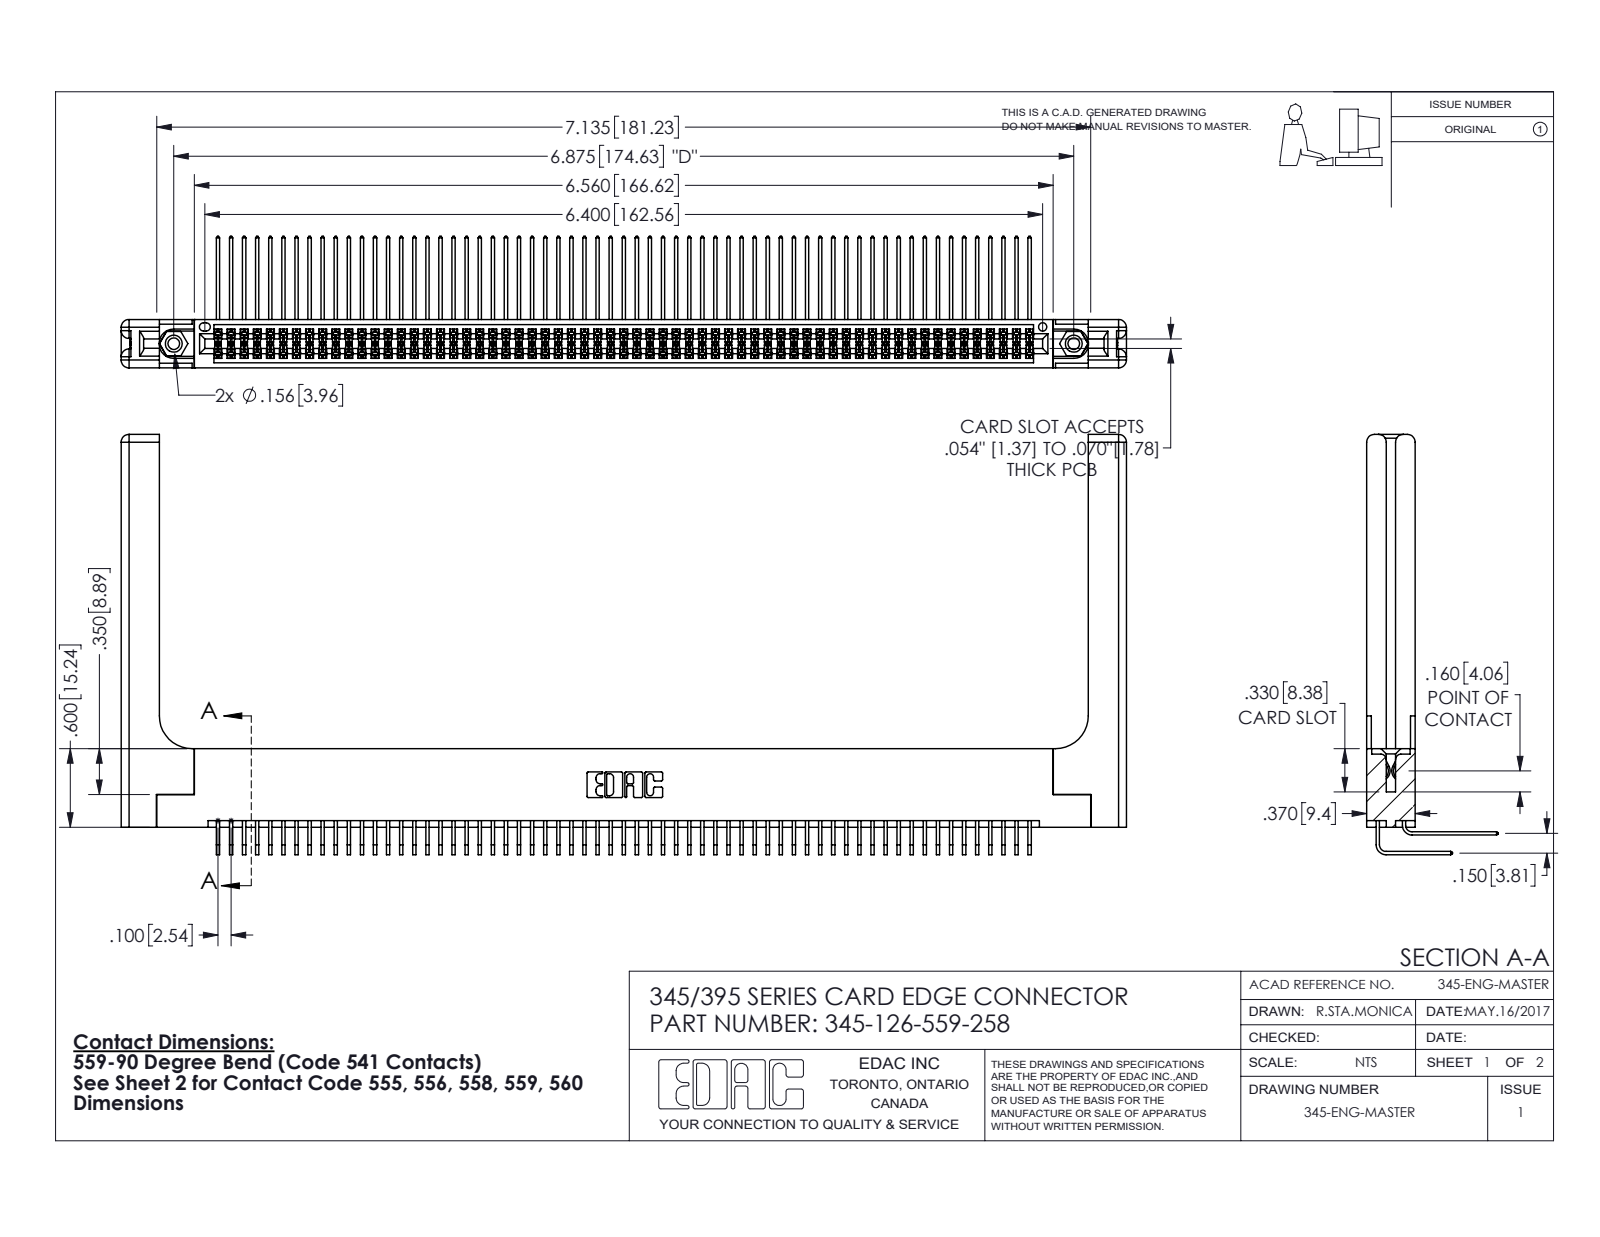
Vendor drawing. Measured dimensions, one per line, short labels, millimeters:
name: 345-250-001_345-250-001-102; 345 Part_Flush Mounting Lugs - 0.156 Dia-TH; 345-292-001_559 Tail - 2; 345-292-001_558 559 Tail - 1 (+2 more)
written by: SolidWorks 2016 (CONFIG_CONTROL_DESIGN)
unit: mm
bodies: 131 solids, 6934 faces (4638 planar, 2236 cylindrical, 60 other)
size: 195 × 81.5 × 25.5
volume: 28 350 mm³; area: 38 250 mm²
holes: 2× ⌀2.3, 2× ⌀3.2, 2× ⌀4, 1× ⌀1.6
bosses: 2× ⌀3.9
rounds: 251× R0.2, 22× R0.3, 16× R1.5, 6× R0.2, 6× R0.8, 3× R0.7, 2× R0.4, 2× R0.5
face distances: 1.8, 7.6, 9.4, 5.1, 2.5, 6.9, 0.6, 5.7, 4.4, 3.8
hole spacings: 6.9, 168.6, 174.6
